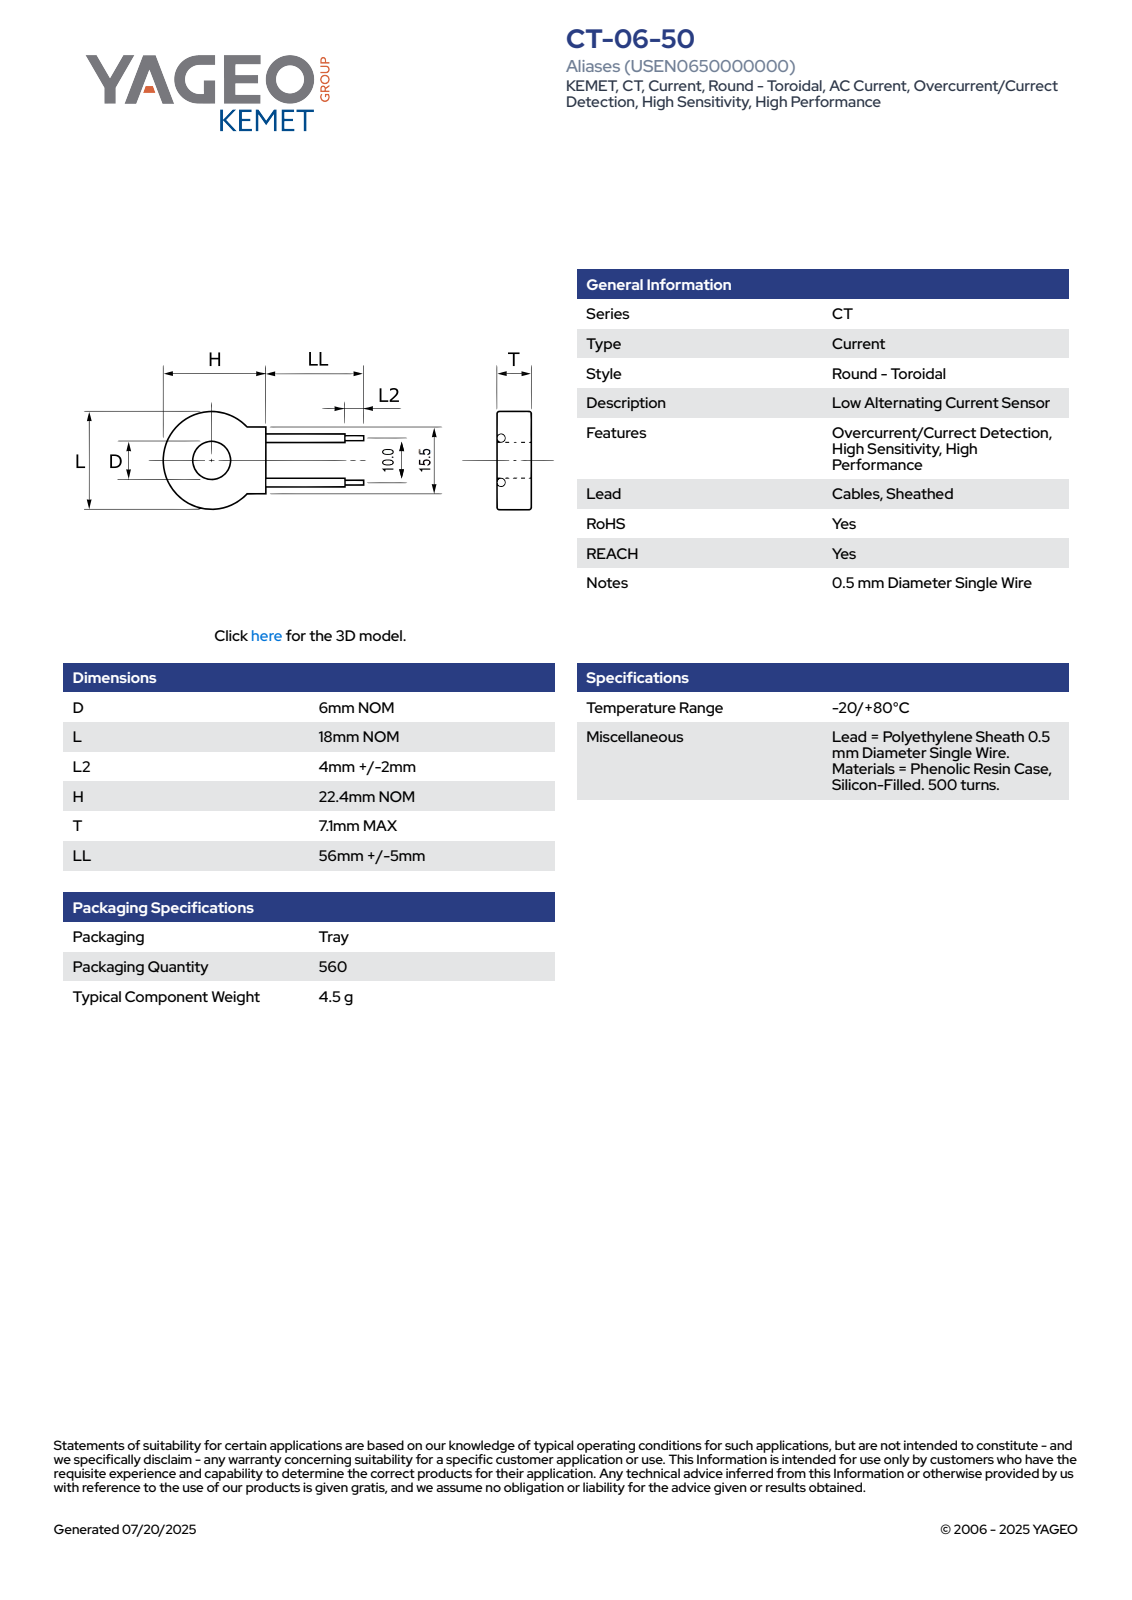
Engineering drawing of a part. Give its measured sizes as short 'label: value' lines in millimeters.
name: SC_CT06_D6L18L26H22.4T7.1LL61
written by: SolidWorks 2014 (AUTOMOTIVE_DESIGN)
unit: mm
bodies: 1 solid, 78 faces (31 planar, 16 cylindrical, 31 other)
size: 83.4 × 18 × 7.1
volume: 2 436 mm³; area: 1 824 mm²
holes: 1× ⌀6
bosses: 2× ⌀1.5, 2× ⌀1
rounds: 1× R8.99, 1× R9
face distances: 7.1, 15.5, 55, 61, 6, 2.54, 4.56, 2.02, 2.93, 4.17
